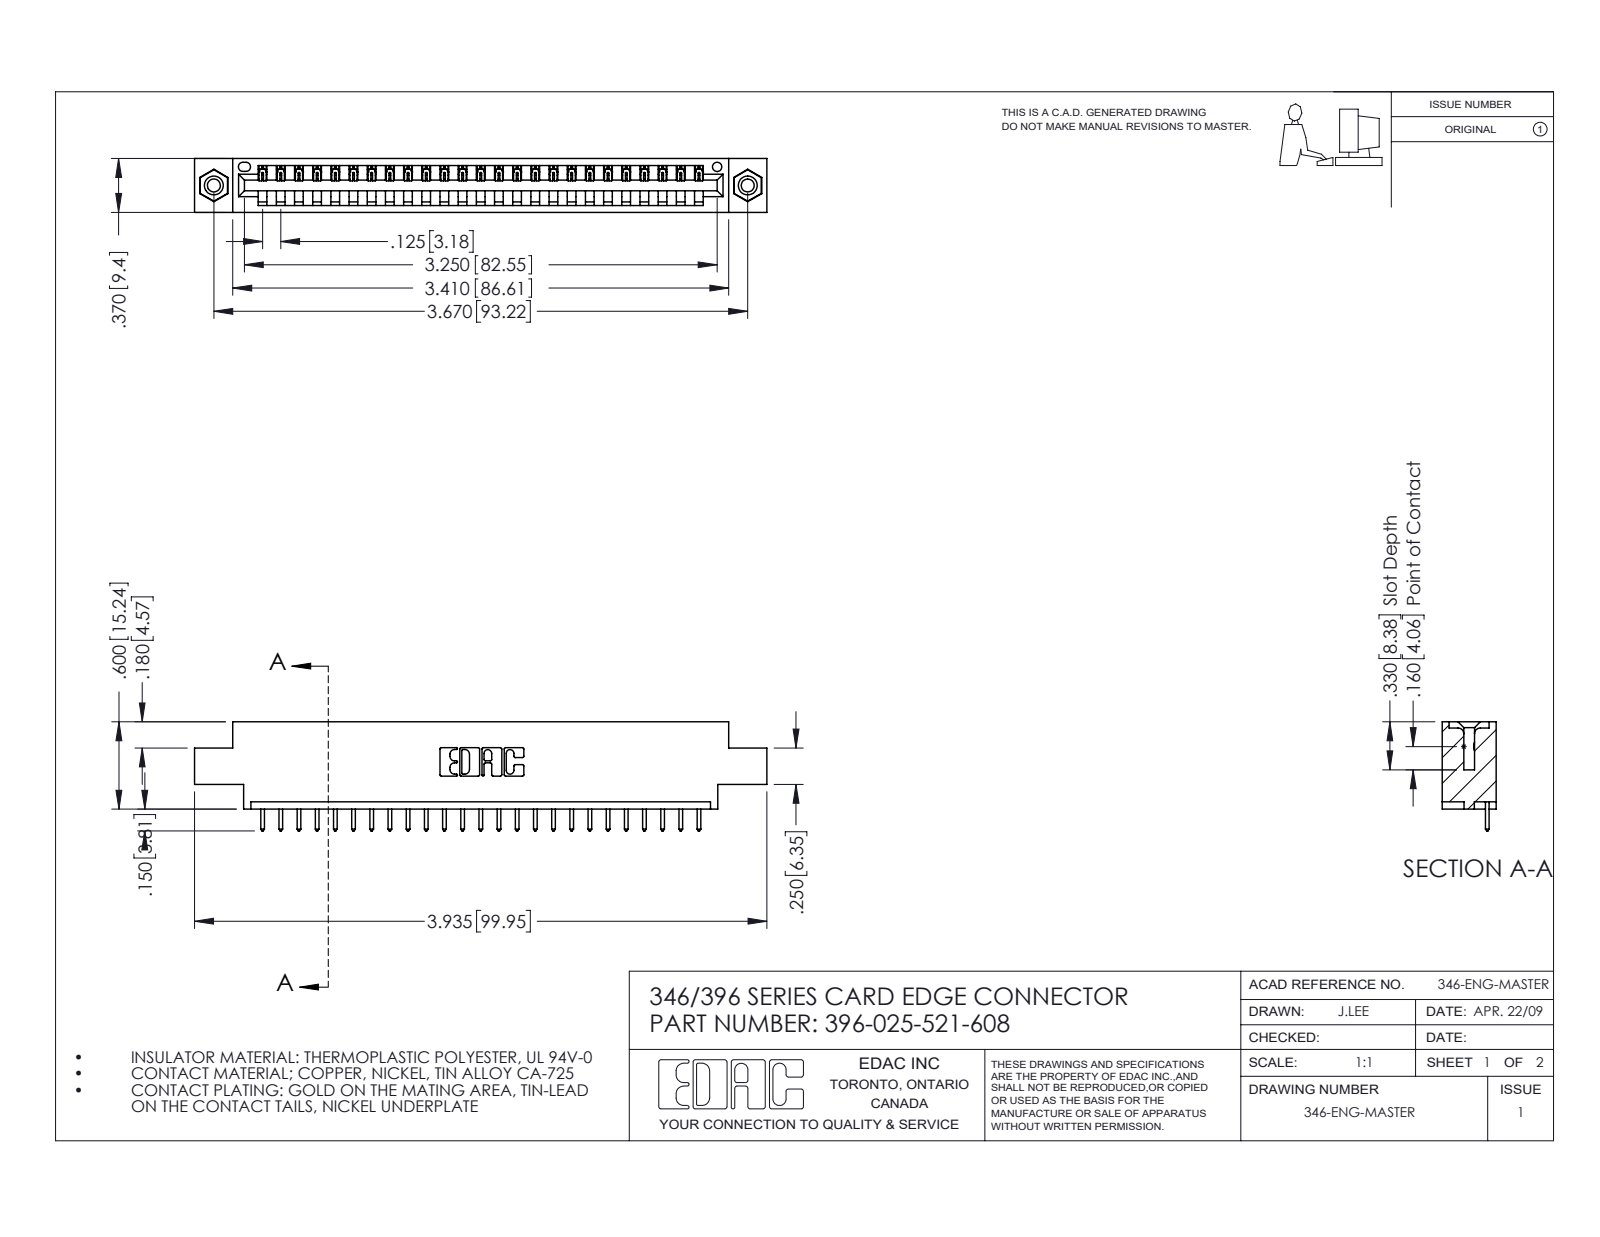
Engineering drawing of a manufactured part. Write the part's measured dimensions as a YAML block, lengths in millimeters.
part_name: "345-292-001_345-293-121; 346 Part_0.170 Offset - 0.156 Dia-TI; 396-025-521-608; 345-250-001_345-250-003-102"
step_written_by: "SolidWorks 2016 (CONFIG_CONTROL_DESIGN)"
units: millimeters
bodies: {solids: 28, faces: 1636, planar: 1112, cylindrical: 508, other: 16}
overall_size: [99.9, 19.1, 9.4]
volume: 9230
surface_area: 11240
round_holes:
  - {diameter: 2.3, count: 2}
  - {diameter: 3.2, count: 2}
  - {diameter: 4, count: 2}
  - {diameter: 1.6, count: 1}
round_bosses_or_shafts:
  - {diameter: 3.9, count: 2}
partial_cylinders:
  - {radius: 0.2, count: 50}
  - {radius: 0.3, count: 50}
  - {radius: 0.3, count: 22}
  - {radius: 0.2, count: 6}
  - {radius: 0.8, count: 6}
  - {radius: 0.7, count: 3}
  - {radius: 0.8, count: 2}
  - {radius: 1, count: 2}
face_to_face_distances: [1.2, 8.2, 9.4, 6.4, 1.8, 7.6, 0.6, 5.6, 3.8, 2.5]
hole_center_spacings: [6.2, 87.9, 93.2]
